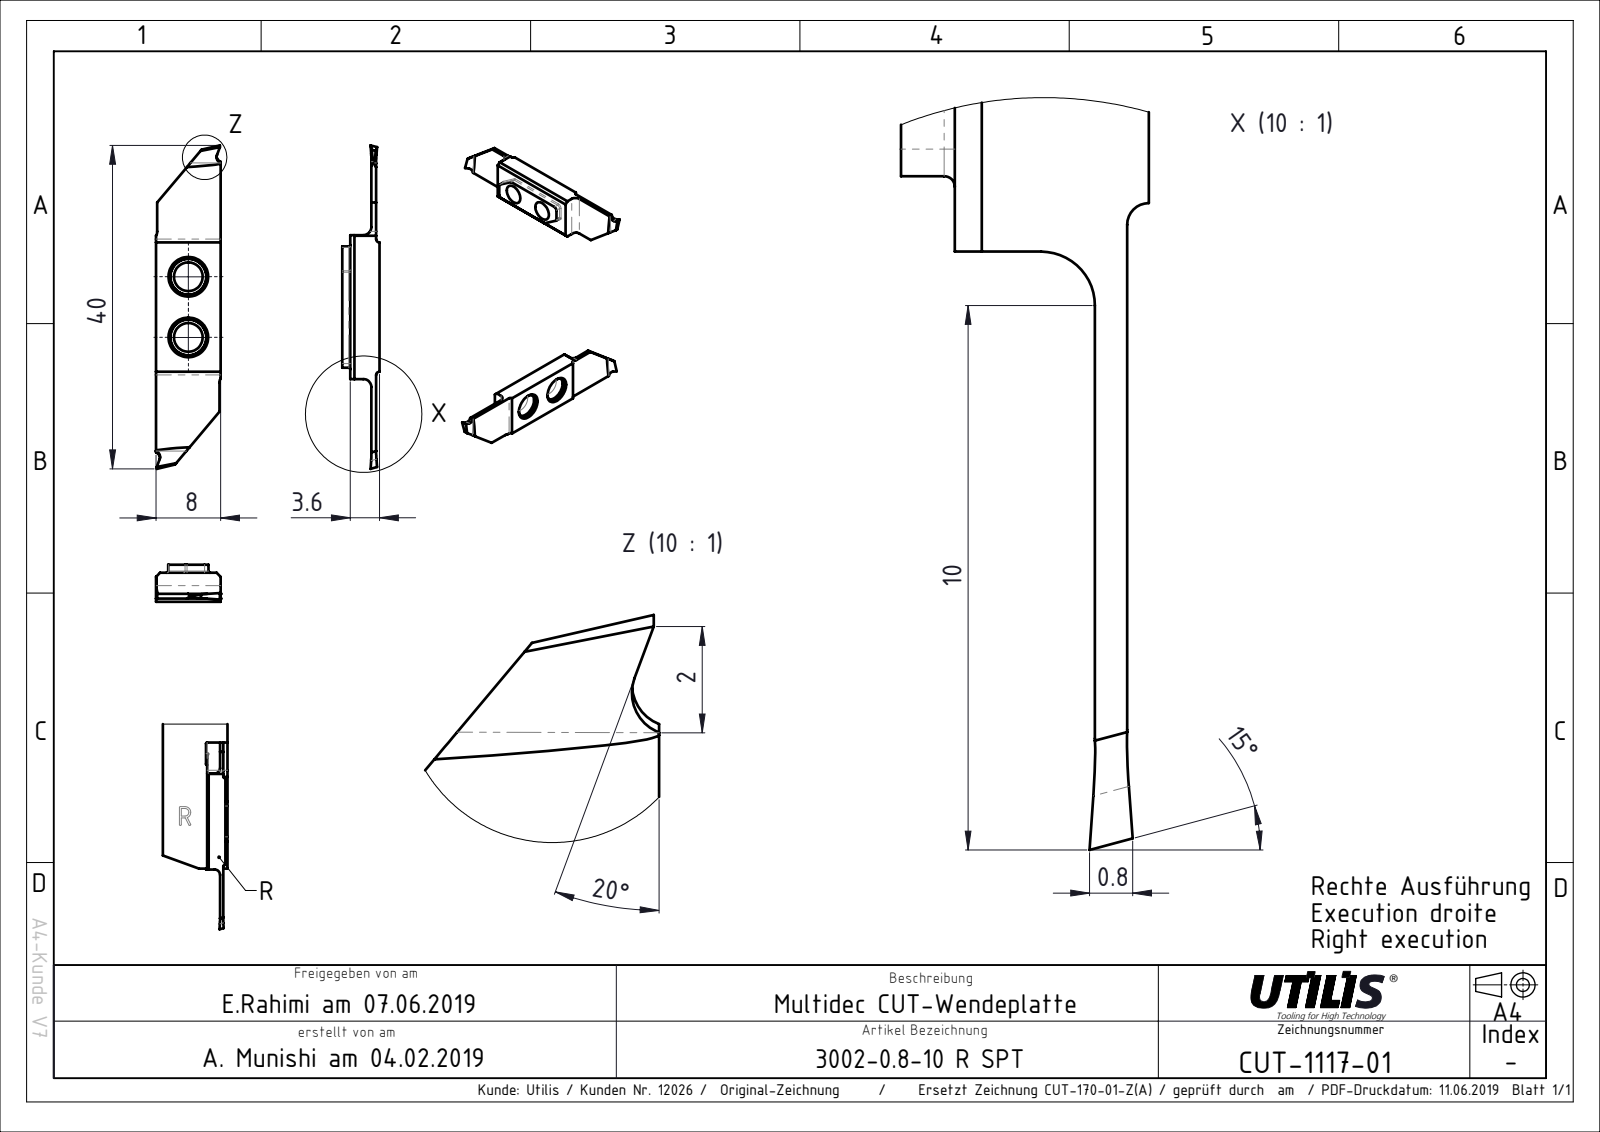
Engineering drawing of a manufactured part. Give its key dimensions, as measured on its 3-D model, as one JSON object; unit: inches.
{"part_name": "CUT-1117; ASME Y14.5", "step_written_by": "FormatWorks Professional (AP242_MANAGED_MODEL_BASED_3D_ENGINEERING_MIM_LF)", "units": "inches", "bodies": {"solids": 1, "faces": 34, "planar": 24, "cylindrical": 10, "other": 0}, "overall_size": [1.575, 0.315, 0.142], "volume_in3": 0.031, "surface_area_in2": 1.2, "round_holes": [[0.14, 2]], "partial_cylinders_radius": [[0.039, 4], [0.016, 2]], "face_to_face_distances": [0.016, 0.023, 0.039, 0.103, 0.126, 0.142, 0.315, 0.701, 0.887, 0.309], "hole_center_spacings": [0.295]}
